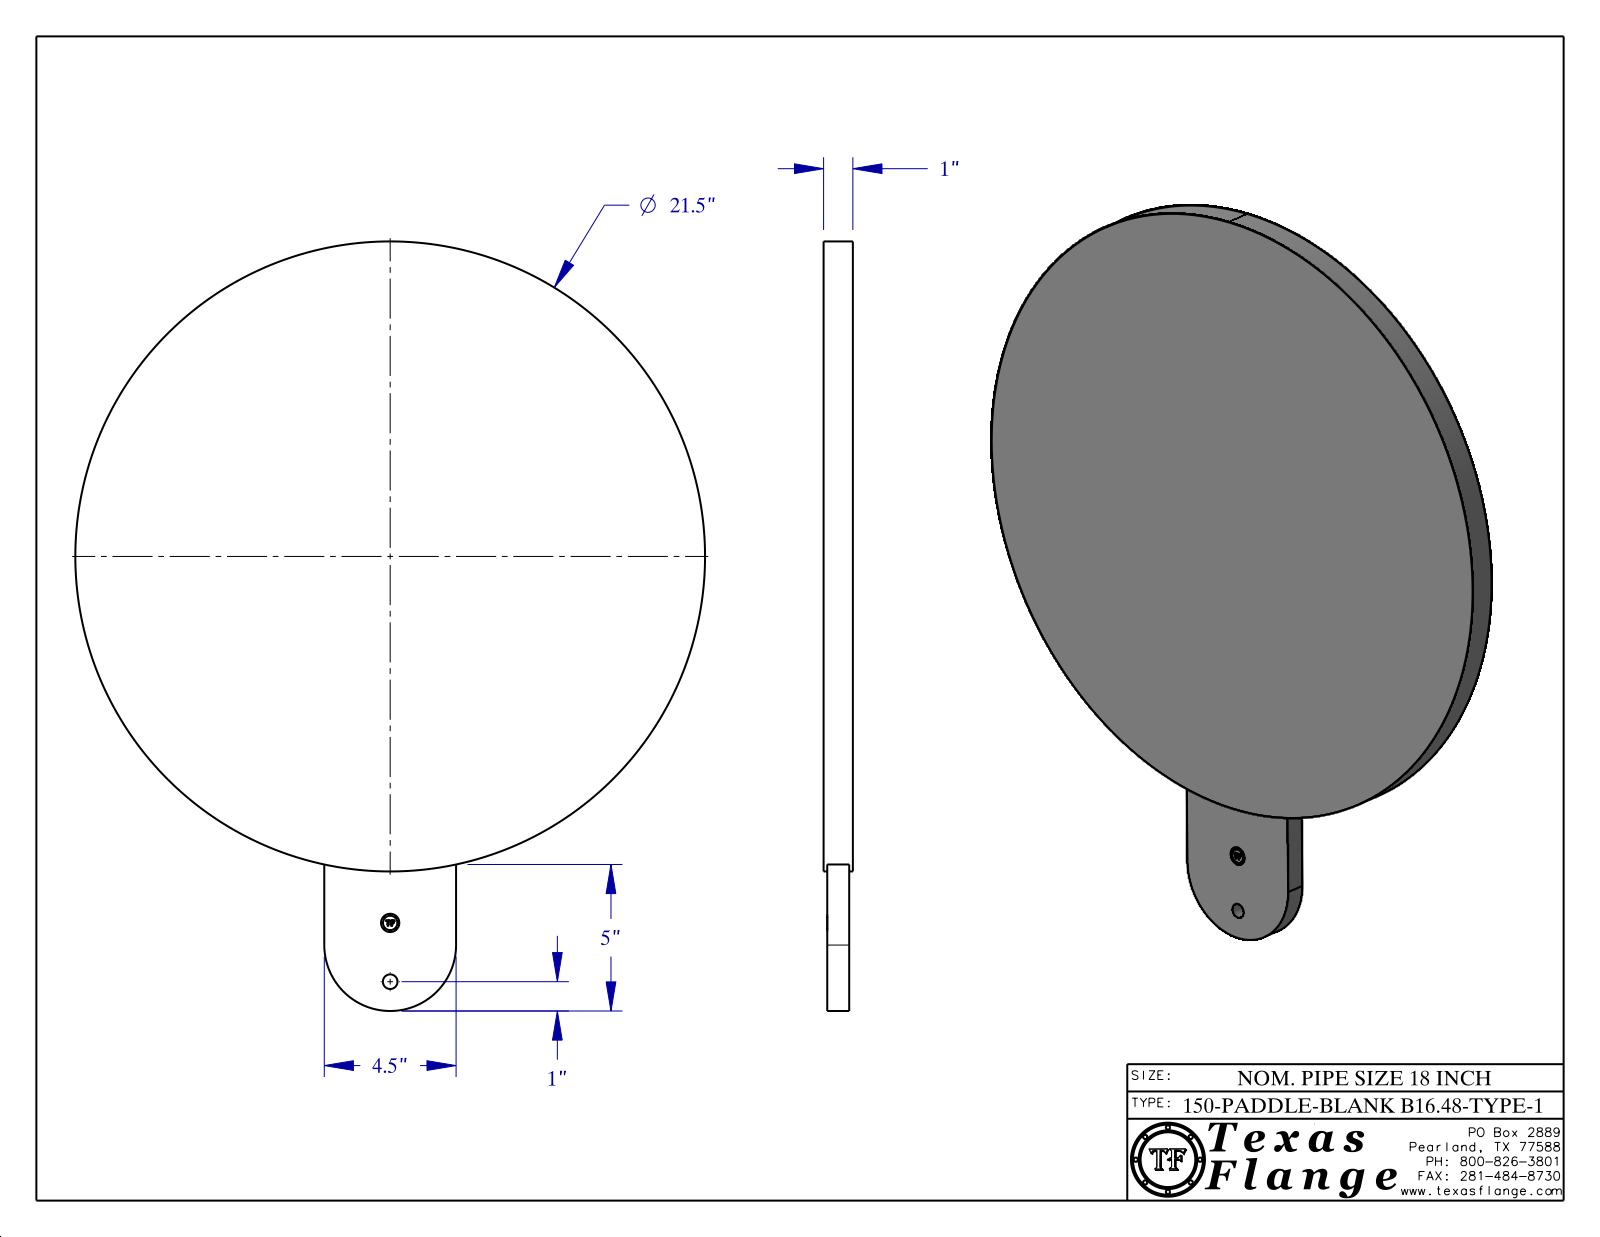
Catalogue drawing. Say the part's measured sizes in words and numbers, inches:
The part is named "18-150-PADDLE-BLANK-B16.48-TYPE-1". Its 3-D file was written by "CATIA V5 STEP AP214 (AUTOMOTIVE_DESIGN)". It is 1 solid with 396 faces: 371 planar, 25 cylindrical and 0 other. Overall it measures 26.262 by 21.5 by 1 inches. Its volume is 377.6 cubic inches and its surface area 839.8 square inches. Round holes: 1 of diameter 0.5, 1 of diameter 0.625. Round bosses or shafts: 8 of diameter 0.038, 1 of diameter 21.5, 1 of diameter 0.492. Partial cylindrical surfaces (rounded edges, fillets, slot ends): 1 of radius 2.25. The main face-to-face distances are 1, 0.125, 0.875, 0.75, 4.5, 0.14, 0.86, 0.735, 0.015, 2.187. The hole center spacings are 2.006.
